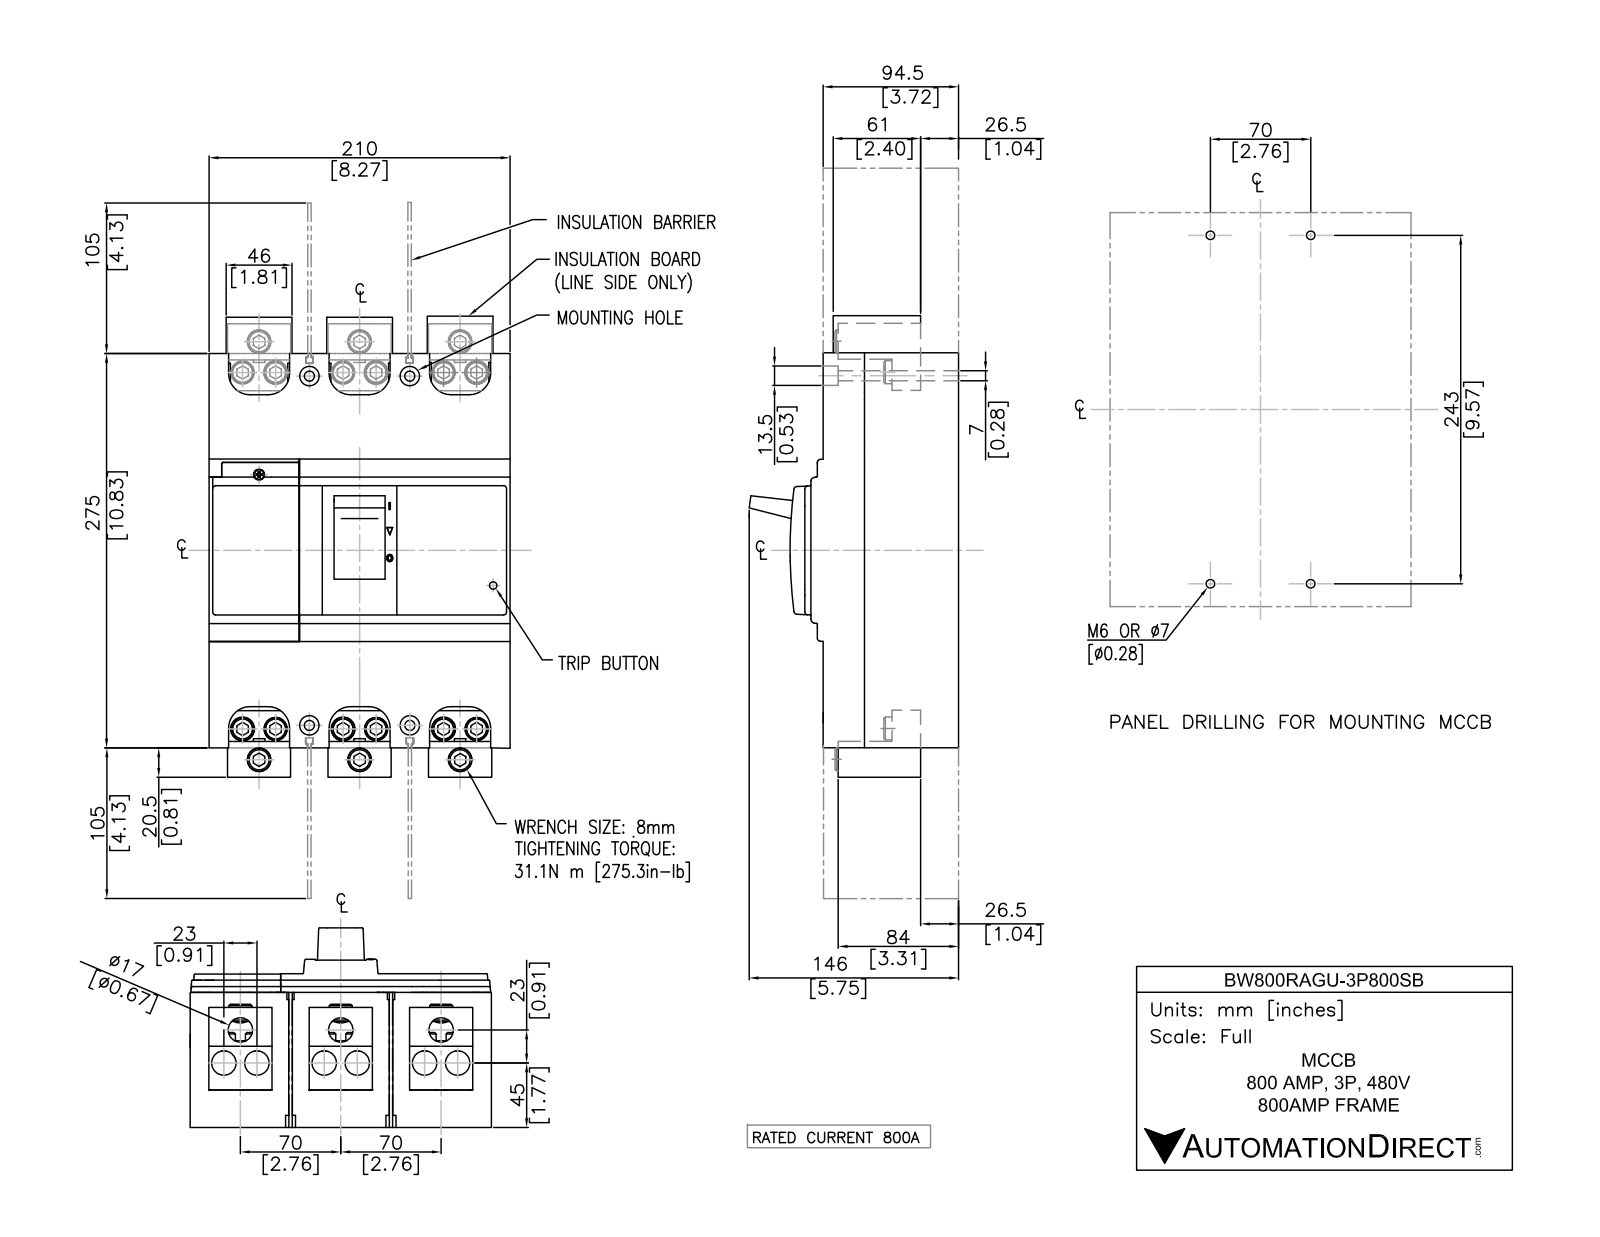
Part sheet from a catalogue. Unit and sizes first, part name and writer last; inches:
Units: inches
Overall size (bounding box): 12.441 × 8.268 × 5.819
Round holes (diameter × count): ⌀0.331 ×12, ⌀0.335 ×12, ⌀0.551 ×12, ⌀0.562 ×12, ⌀0.669 ×9, ⌀0.472 ×6, ⌀0.571 ×6, ⌀0.138 ×4, ⌀0.276 ×4, ⌀0.531 ×4, ⌀0.205 ×1
Round bosses / shafts (diameter × count): ⌀0.63 ×18, ⌀0.531 ×12, ⌀0.512 ×12, ⌀0.315 ×12
Partial cylindrical surfaces — rounded edges, fillets, slot ends (radius × count): R0.591 ×12
Main face-to-face distances: 2.756, 8.268, 3.72, 1.732, 4.213, 0.492, 3.169, 2.244, 1.043, 2.677
Hole centre spacings: 2.756, 0.463, 0.96, 9.676, 0.906, 1.378, 5.512, 9.666
Volume: 337.8 in³ · Surface area: 638.7 in²
Bodies: 50 solids, 987 faces (517 planar, 302 cylindrical, 168 other)
Part name (STEP PRODUCT): BW800RAGU-3P800SB
STEP written by: SolidWorks 2019 (CONFIG_CONTROL_DESIGN)
